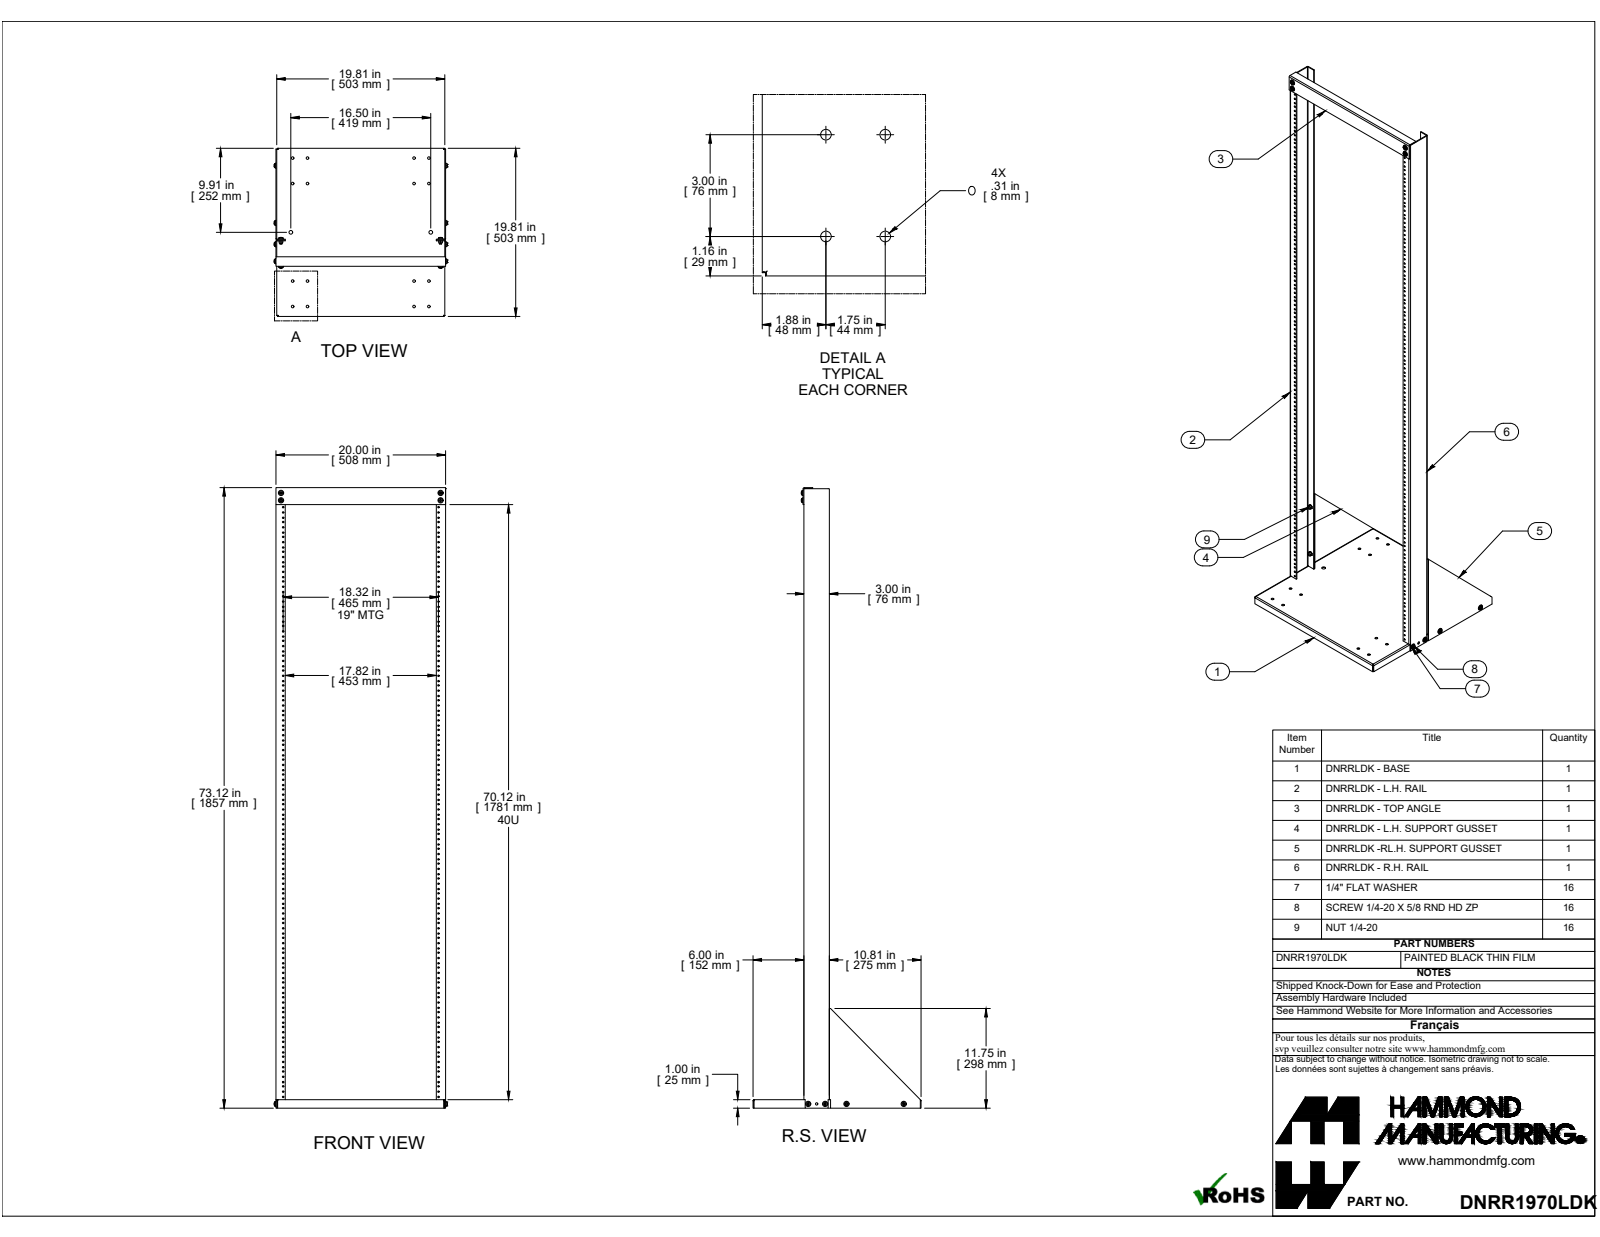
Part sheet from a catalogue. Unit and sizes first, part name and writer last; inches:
Units: inches
Overall size (bounding box): 73.125 × 20.398 × 19.812
Round holes (diameter × count): ⌀0.177 ×240, ⌀0.313 ×18, ⌀0.281 ×15, ⌀0.196 ×12, ⌀0.282 ×12, ⌀0.437 ×2
Round bosses / shafts (diameter × count): ⌀0.468 ×12, ⌀0.25 ×12, ⌀0.625 ×6, ⌀0.625 ×6
Partial cylindrical surfaces — rounded edges, fillets, slot ends (radius × count): R0.048 ×11, R0.143 ×11, R0.156 ×4
Main face-to-face distances: 0.095, 0.095, 19.907, 19.812, 20.002, 3, 2.905, 2.81, 2.905, 0.19
Hole centre spacings: 1.75, 3.5, 5.25, 3, 7, 8.75, 10.5, 0.625
Volume: 132.6 in³ · Surface area: 2 869 in²
Bodies: 54 solids, 1086 faces (584 planar, 398 cylindrical, 104 other)
Part name (STEP PRODUCT): DNRR1970LDK
STEP written by: SolidWorks 2019 (CONFIG_CONTROL_DESIGN)
